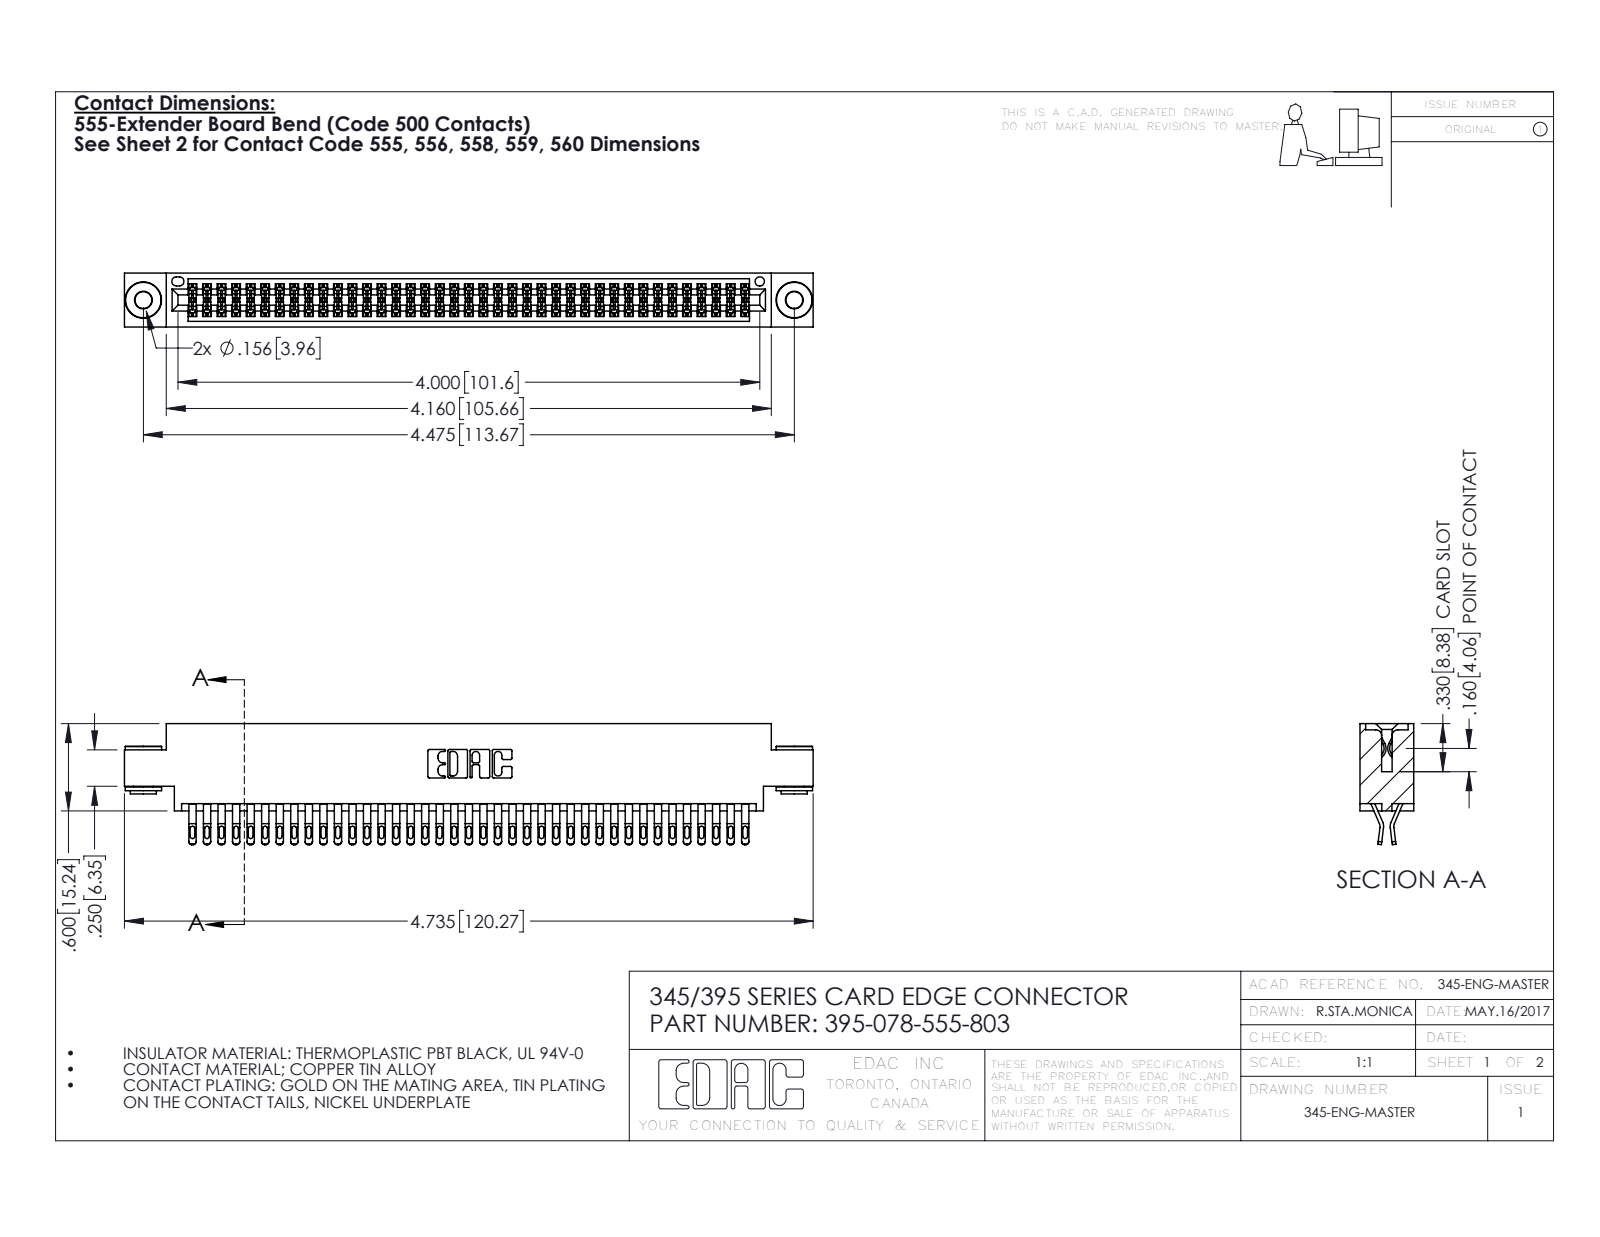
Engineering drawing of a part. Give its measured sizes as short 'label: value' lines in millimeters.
name: 345-250-002_345-250-002-102; 345-292-001_555 Tail; 345 Part_0.170 Offset - 0.156 Dia-TH; 395-078-555-803
written by: SolidWorks 2016 (CONFIG_CONTROL_DESIGN)
unit: mm
bodies: 81 solids, 4536 faces (2512 planar, 2016 cylindrical, 8 other)
size: 120.3 × 21.1 × 9.4
volume: 11 800 mm³; area: 18 500 mm²
holes: 2× ⌀2.9, 2× ⌀4, 1× ⌀1.6
bosses: 2× ⌀6.4, 2× ⌀4.6, 2× ⌀3.5
rounds: 195× R0.4, 156× R0.5, 117× R0.2, 22× R0.3, 6× R0.2, 6× R0.8, 3× R0.7, 2× R0.3
face distances: 1.8, 7.6, 9.4, 0.6, 5.1, 2.5, 6.9, 5.7, 4.4, 3.8
hole spacings: 6.9, 107.7, 113.7
